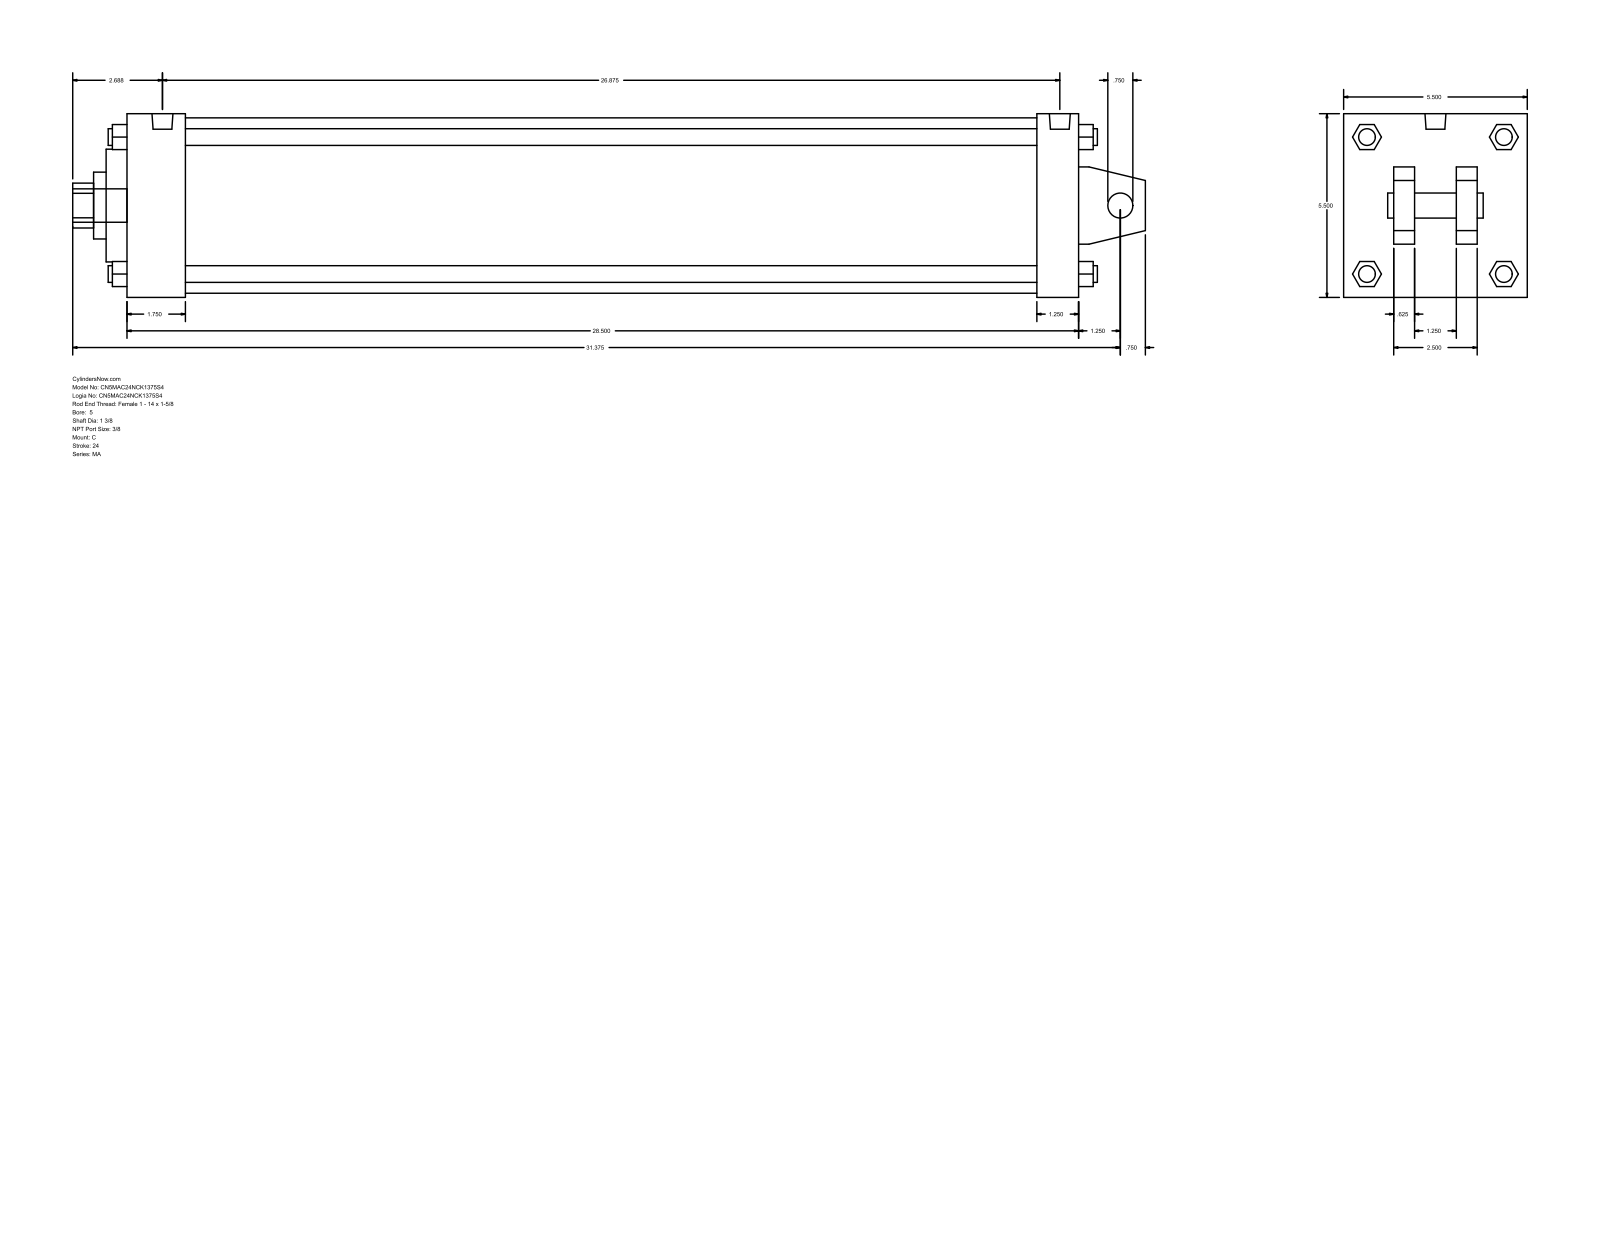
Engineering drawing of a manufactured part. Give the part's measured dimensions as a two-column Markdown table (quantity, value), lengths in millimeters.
| quantity | value |
| --- | --- |
| part name | MA_C__0500_1.375 |
| STEP written by | GSSL Pune (CONFIG_CONTROL_DESIGN) |
| units | millimeters |
| bodies | 0 solids, 141 faces (109 planar, 32 cylindrical, 0 other) |
| overall size | 815.98 × 139.7 × 139.7 |
| round holes (diameter × count) | 19.05 × 1, 34.92 × 1, 50.8 × 1, 85.72 × 1, 133.35 × 1 |
| round bosses / shafts (diameter × count) | 12.7 × 4, 11.11 × 4, 15.93 × 2, 25.4 × 1 |
| partial cylindrical surfaces (radius × count) | 17.06 × 1 |
| main face-to-face distances | 139.7, 723.9, 15.87, 692.15, 31.75, 44.45, 647.7, 679.45, 38.1, 101.6 |
